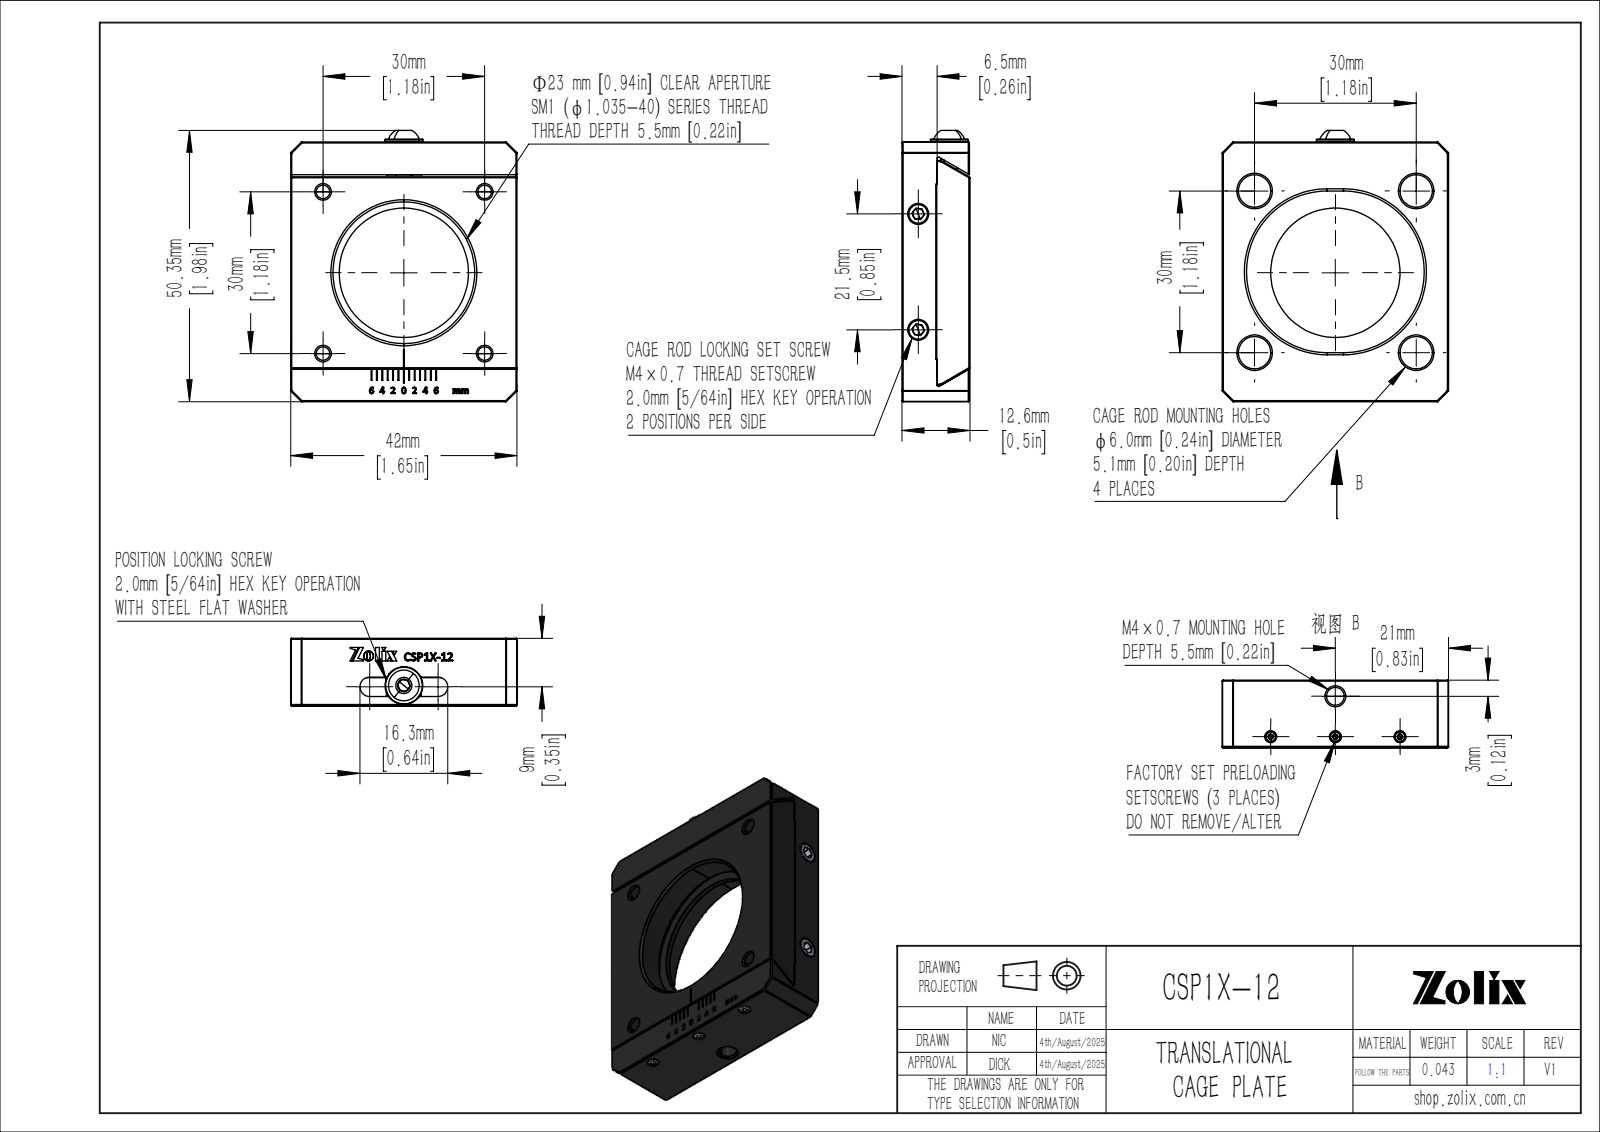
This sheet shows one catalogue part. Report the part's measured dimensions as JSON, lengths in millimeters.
{"part_name": "CSP1X-12", "step_written_by": "SolidWorks 2020 (CONFIG_CONTROL_DESIGN)", "units": "millimeters", "bodies": {"solids": 10, "faces": 917, "planar": 475, "cylindrical": 113, "other": 329}, "overall_size": [50.35, 42, 12.6], "volume_mm3": 15868, "surface_area_mm2": 11117, "round_holes": [[2.5, 5], [6, 4], [1.6, 3], [3.3, 3], [24, 1], [26.29, 1], [27.5, 1]], "round_bosses_or_shafts": [[2, 3], [4, 2], [7, 1], [3, 1]], "partial_cylinders_radius": [[0.2, 42], [0.3, 2], [1.8, 2], [15, 2]], "face_to_face_distances": [6.25, 6.35, 12.6, 42, 12.5, 48.2, 6, 6.5, 6.1, 0.34], "hole_center_spacings": [30, 21.21, 42.43, 12, 12.13, 14.15, 21.1, 21.33]}
